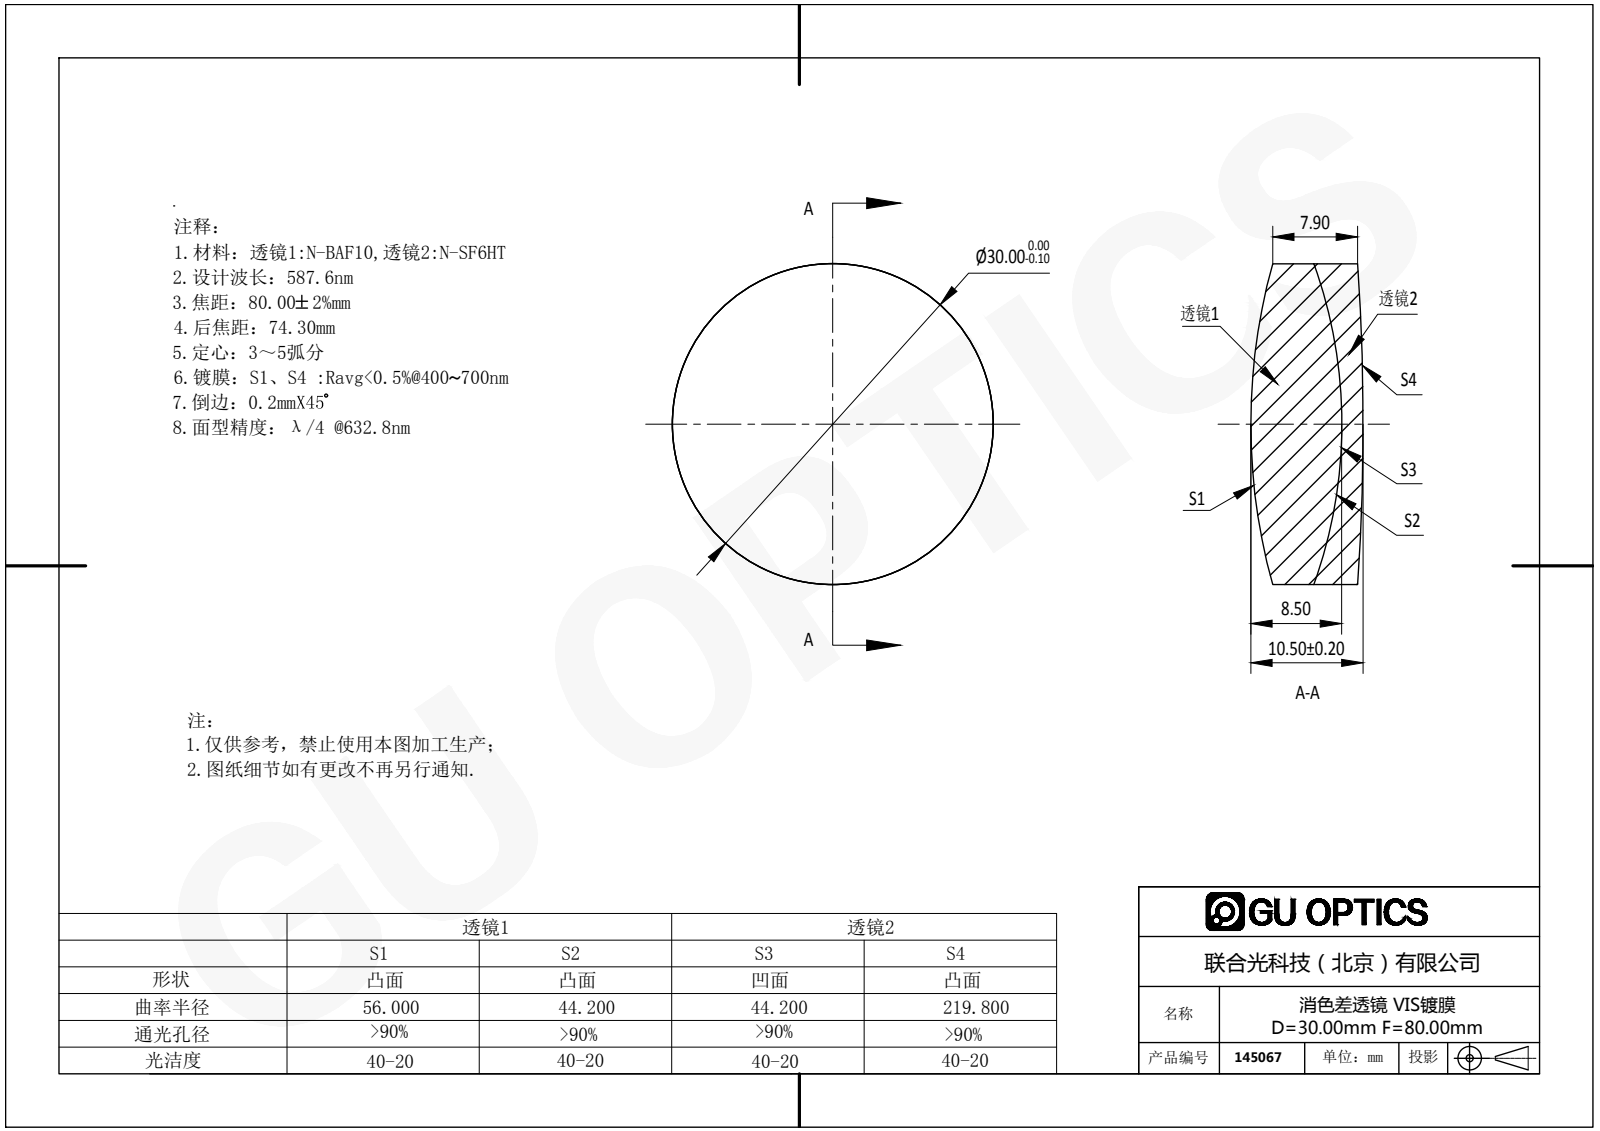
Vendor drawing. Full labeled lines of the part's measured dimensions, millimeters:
Part name (STEP PRODUCT): 145067
STEP written by: SolidWorks 2016 (AUTOMOTIVE_DESIGN)
Units: millimetres
Bodies: 2 solids, 12 faces (0 planar, 4 cylindrical, 8 other)
Overall size (bounding box): 30 × 30 × 10.5
Volume: 6 522 mm³ · Surface area: 3 633 mm²
Round bosses / shafts (diameter × count): ⌀30 ×1
